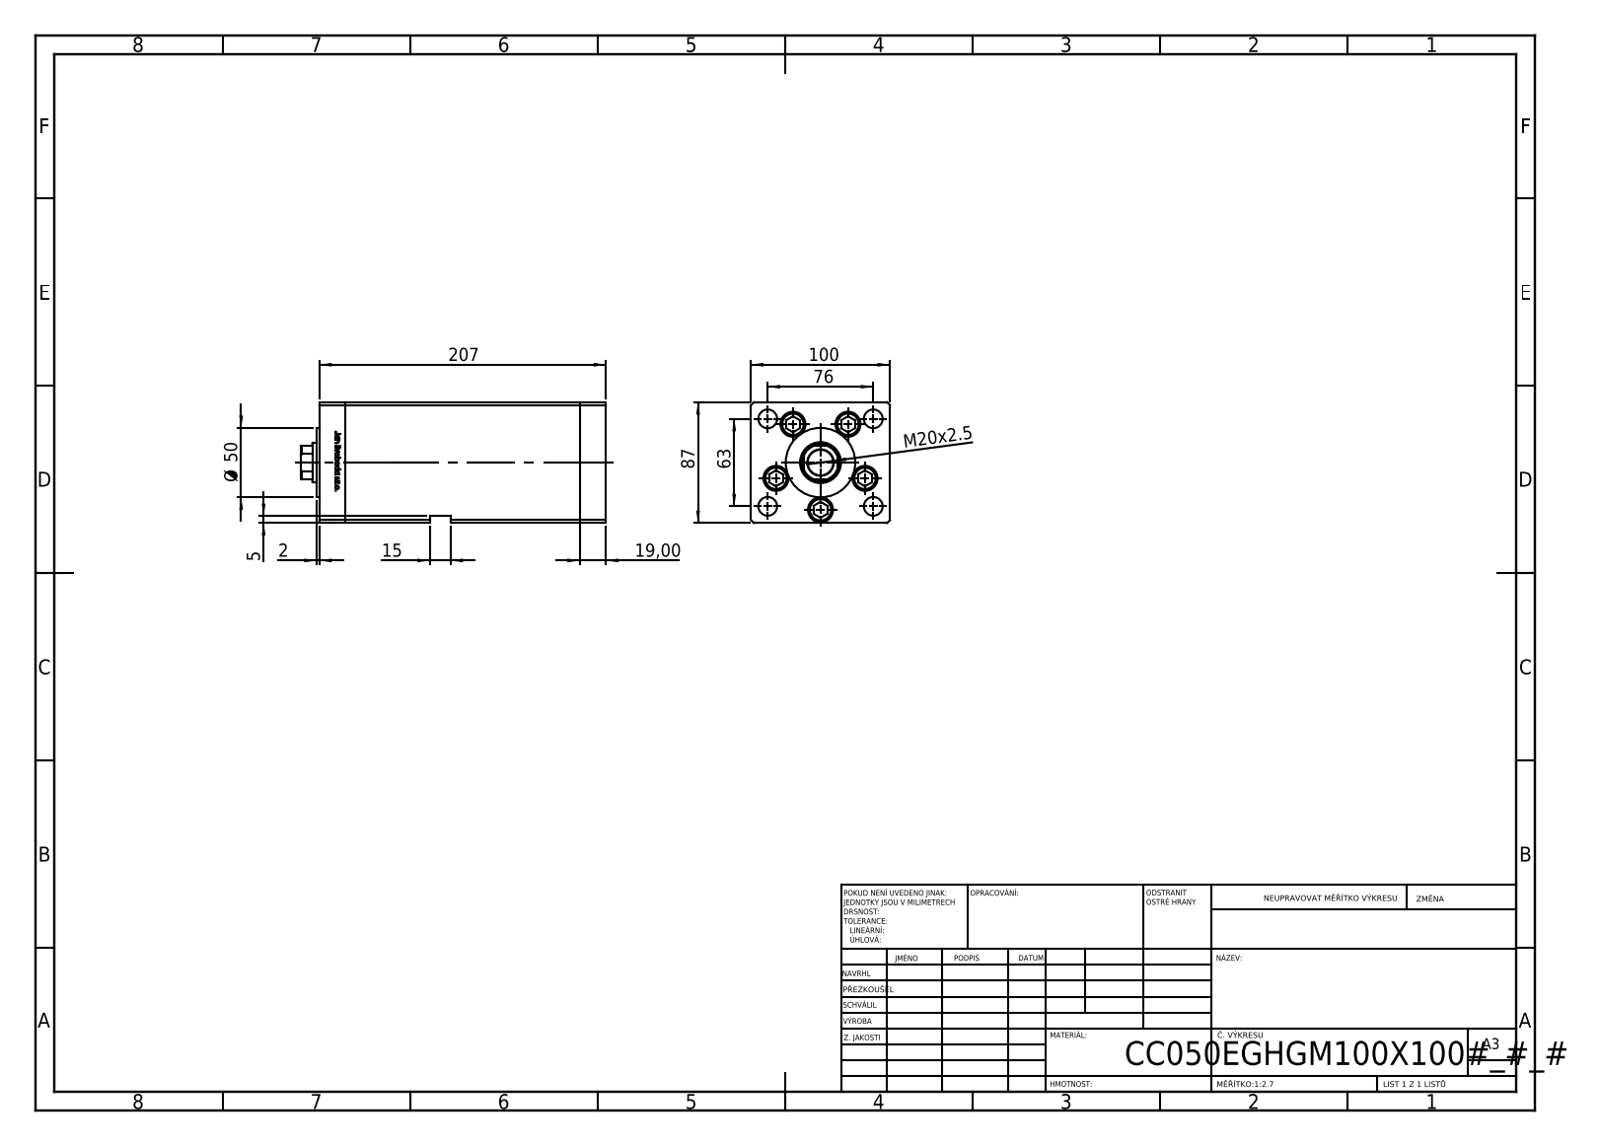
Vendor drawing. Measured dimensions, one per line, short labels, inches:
name: ALLEN BOLT; V220C_E MIDDLE; V220C_VC_E; V220C_FRONT_E (+1 more)
written by: SolidWorks 2019 (CONFIG_CONTROL_DESIGN)
unit: in
bodies: 14 solids, 1212 faces (473 planar, 165 cylindrical, 574 other)
size: 8.642 × 3.937 × 3.425
volume: 92.02 in³; area: 362.5 in²
holes: 11× ⌀0.531, 5× ⌀0.709, 5× ⌀0.728, 4× ⌀0.492, 2× ⌀0.079, 2× ⌀0.518, 1× ⌀1.102, 1× ⌀1.161
bosses: 5× ⌀0.669, 5× ⌀0.315, 1× ⌀1.969
rounds: 2× R0.037, 1× R0.531
face distances: 3.937, 3.425, 0.748, 6.634, 7.382, 1.348, 8.13, 0.6, 6.033, 6.781
hole spacings: 1.339, 0.732, 1.561, 1.943, 2.281, 0.828, 1.499, 1.546
